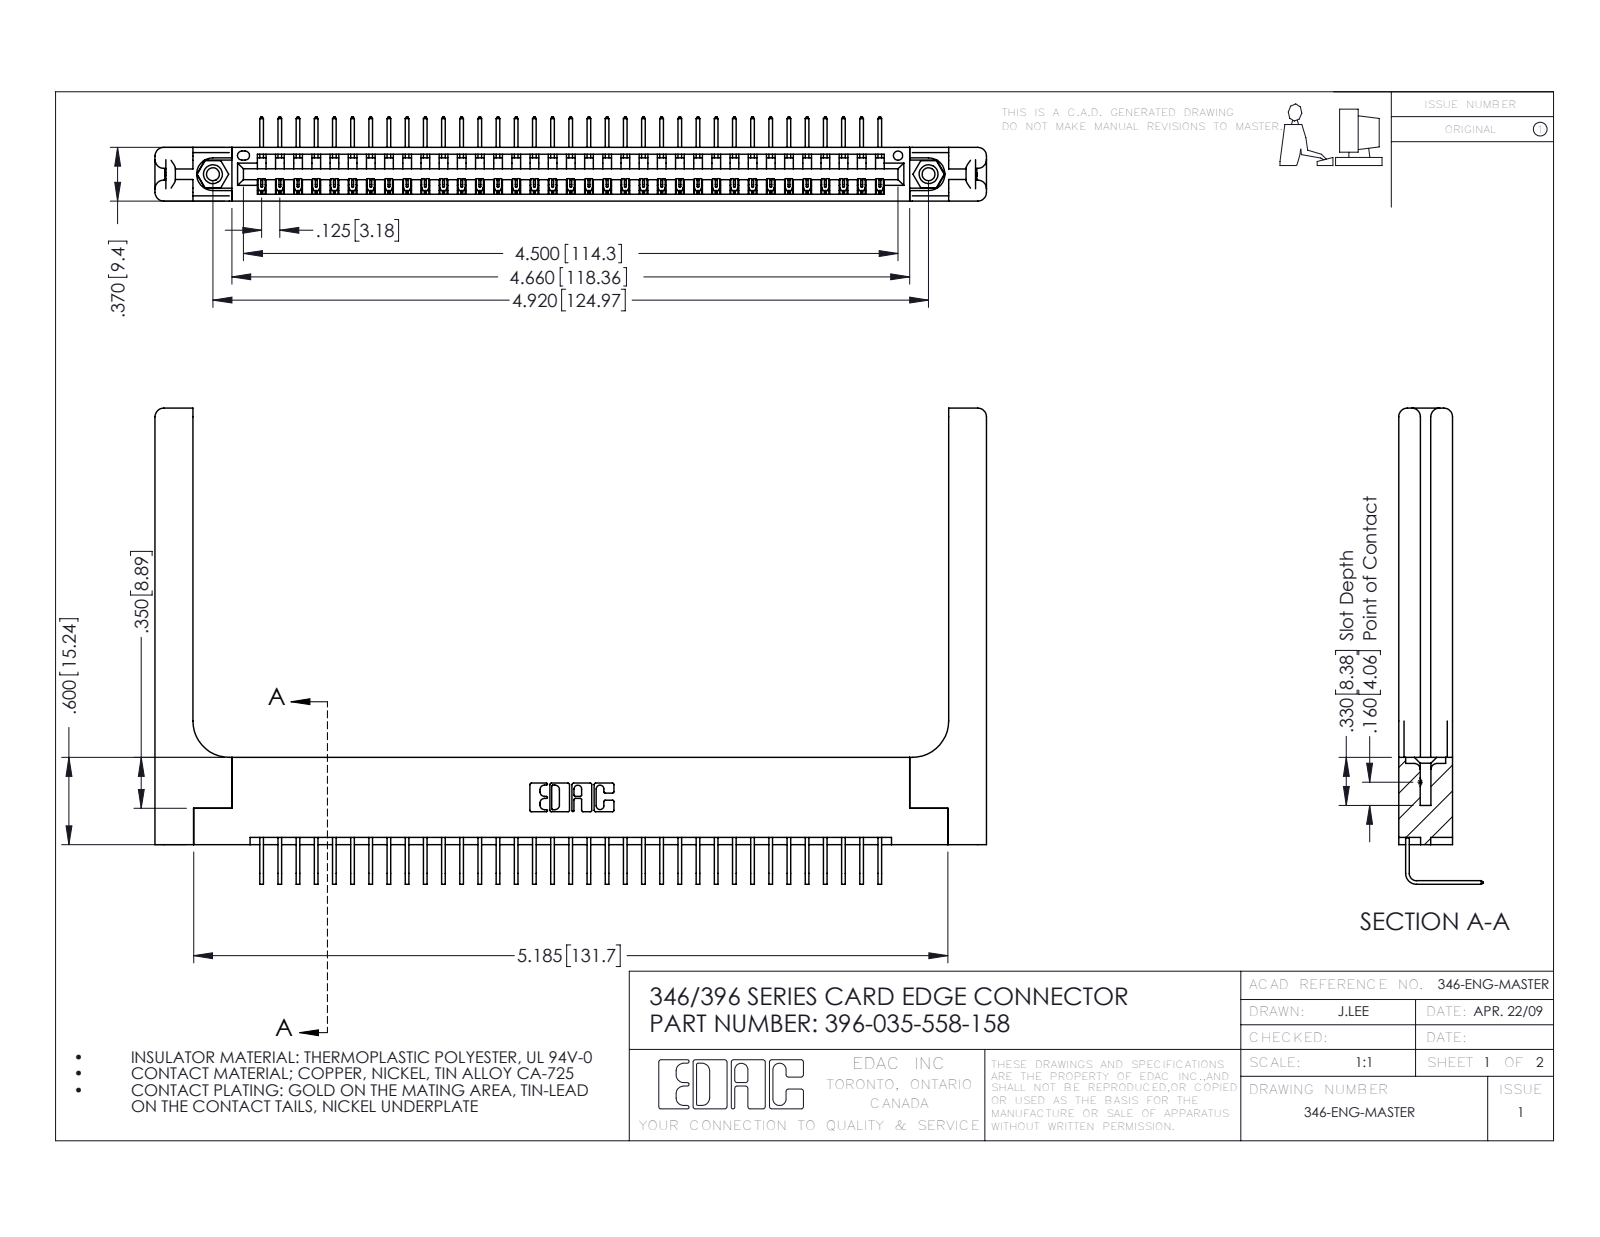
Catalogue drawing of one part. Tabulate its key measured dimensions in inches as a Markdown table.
| quantity | value |
| --- | --- |
| part name | 346 Part_Flush Mounting Lugs - 0.156 Dia-TH; 346-220-058_345-220-058; 345-250-001_345-250-001-102; 345-292-001_558 Tail - 2 (+1 more) |
| STEP written by | SolidWorks 2016 (CONFIG_CONTROL_DESIGN) |
| units | inches |
| bodies | 40 solids, 2478 faces (1694 planar, 724 cylindrical, 60 other) |
| overall size | 5.716 × 3.273 × 0.58 |
| volume | 1.311 in³ |
| surface area | 36.03 in² |
| round holes (diameter × count) | 0.089 × 2, 0.125 × 2, 0.156 × 2, 0.064 × 1 |
| round bosses / shafts (diameter × count) | 0.155 × 2 |
| partial cylindrical surfaces (radius × count) | 0.006 × 70, 0.01 × 22, 0.06 × 16, 0.007 × 6, 0.031 × 6, 0.026 × 3, 0.03 × 2, 0.031 × 2 |
| main face-to-face distances | 0.37, 0.322, 0.048, 0.072, 0.148, 0.15, 0.25, 0.025, 0.298, 0.222 |
| hole center spacings | 0.246, 4.711, 4.92 |
